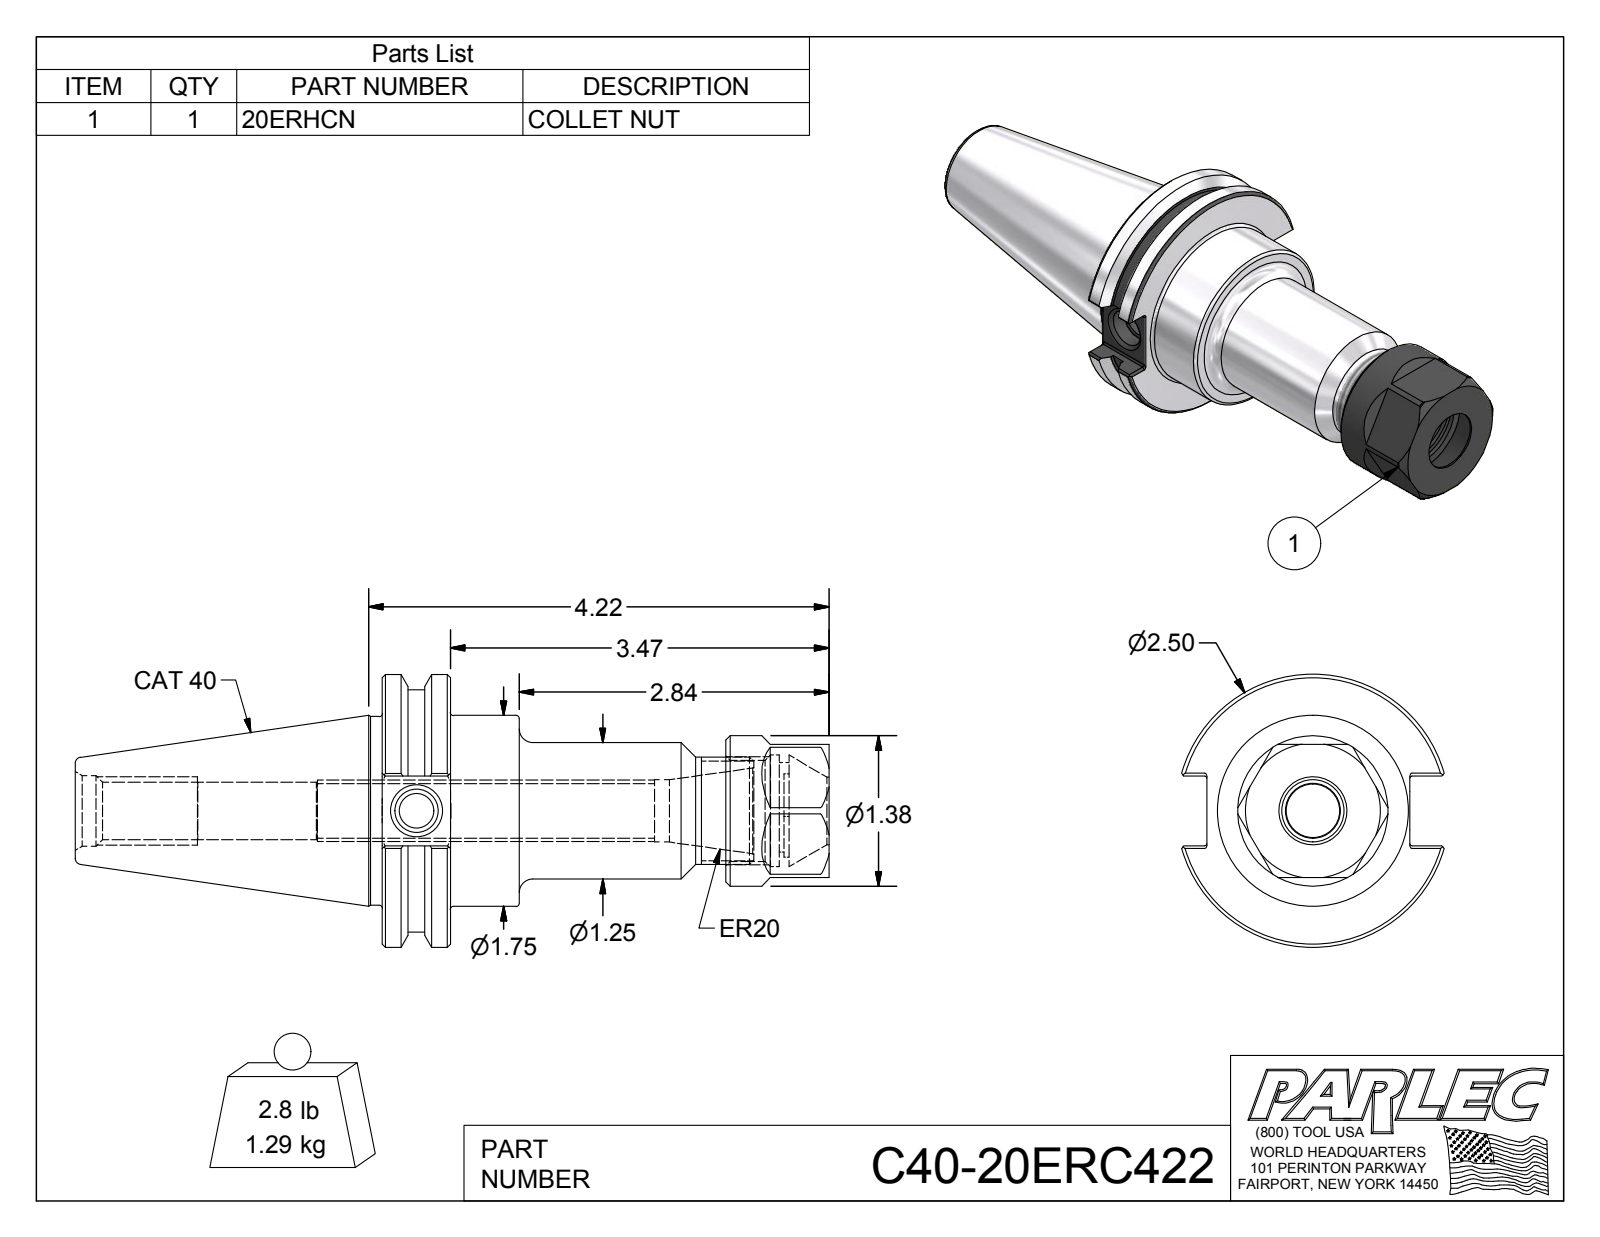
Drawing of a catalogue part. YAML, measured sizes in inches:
part_name: "C40-20ER4-1; 20ERHCN; C40-20ERC422"
step_written_by: "Autodesk Inventor 2016 (AUTOMOTIVE_DESIGN)"
units: inches
bodies: {solids: 2, faces: 127, planar: 50, cylindrical: 35, other: 42}
overall_size: [6.907, 2.5, 2.404]
volume: 10.04
surface_area: 55.64
round_holes:
  - {diameter: 0.315, count: 1}
  - {diameter: 0.399, count: 1}
  - {diameter: 0.502, count: 1}
  - {diameter: 0.525, count: 1}
  - {diameter: 0.527, count: 1}
  - {diameter: 0.57, count: 1}
  - {diameter: 0.62, count: 1}
  - {diameter: 0.648, count: 1}
  - {diameter: 0.82, count: 1}
  - {diameter: 0.925, count: 1}
  - {diameter: 1.024, count: 1}
round_bosses_or_shafts:
  - {diameter: 2.5, count: 1}
  - {diameter: 2.219, count: 1}
  - {diameter: 1.75, count: 1}
  - {diameter: 1.73, count: 1}
  - {diameter: 1.378, count: 1}
  - {diameter: 1.25, count: 1}
  - {diameter: 0.984, count: 1}
partial_cylinders:
  - {radius: 0.02, count: 12}
  - {radius: 0.423, count: 1}
face_to_face_distances: [0.625, 1.22, 4.095, 3.47, 3.15, 2.525, 0.945, 1.255, 0.63, 1.895]
hole_center_spacings: [0.037]
